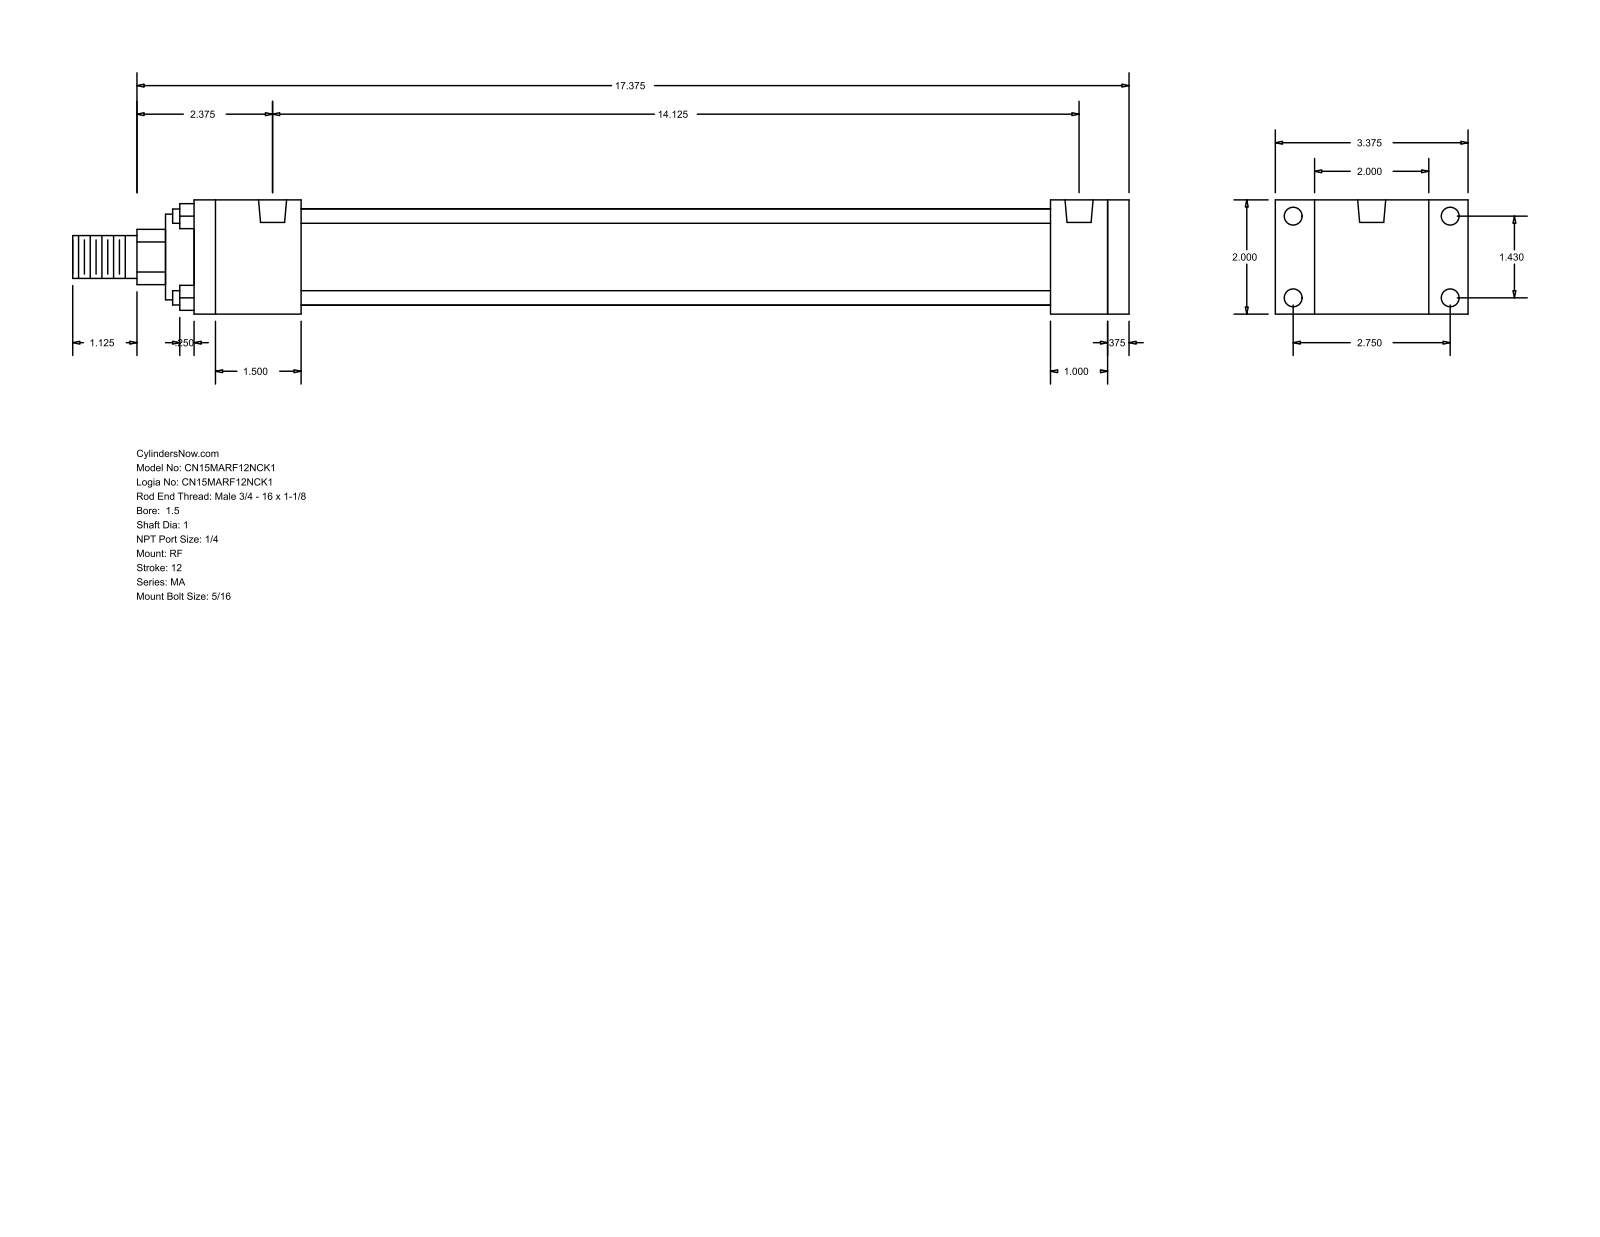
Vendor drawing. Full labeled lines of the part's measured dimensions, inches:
Part name (STEP PRODUCT): MA_RF__0150_1
STEP written by: GSSL Pune (CONFIG_CONTROL_DESIGN)
Units: inches
Bodies: 0 solids, 92 faces (64 planar, 28 cylindrical, 0 other)
Overall size (bounding box): 18.5 × 3.375 × 2
Round holes (diameter × count): ⌀0.313 ×8, ⌀0.492 ×2
Round bosses / shafts (diameter × count): ⌀0.25 ×4, ⌀1.69 ×1, ⌀1.5 ×1, ⌀1 ×1, ⌀0.75 ×1
Partial cylindrical surfaces — rounded edges, fillets, slot ends (radius × count): R0.484 ×1
Main face-to-face distances: 2, 0.375, 16.375, 16, 1, 15, 1.375, 1.875, 13.125, 14.125
Hole centre spacings: 1.43, 2.75, 3.099, 14.125
